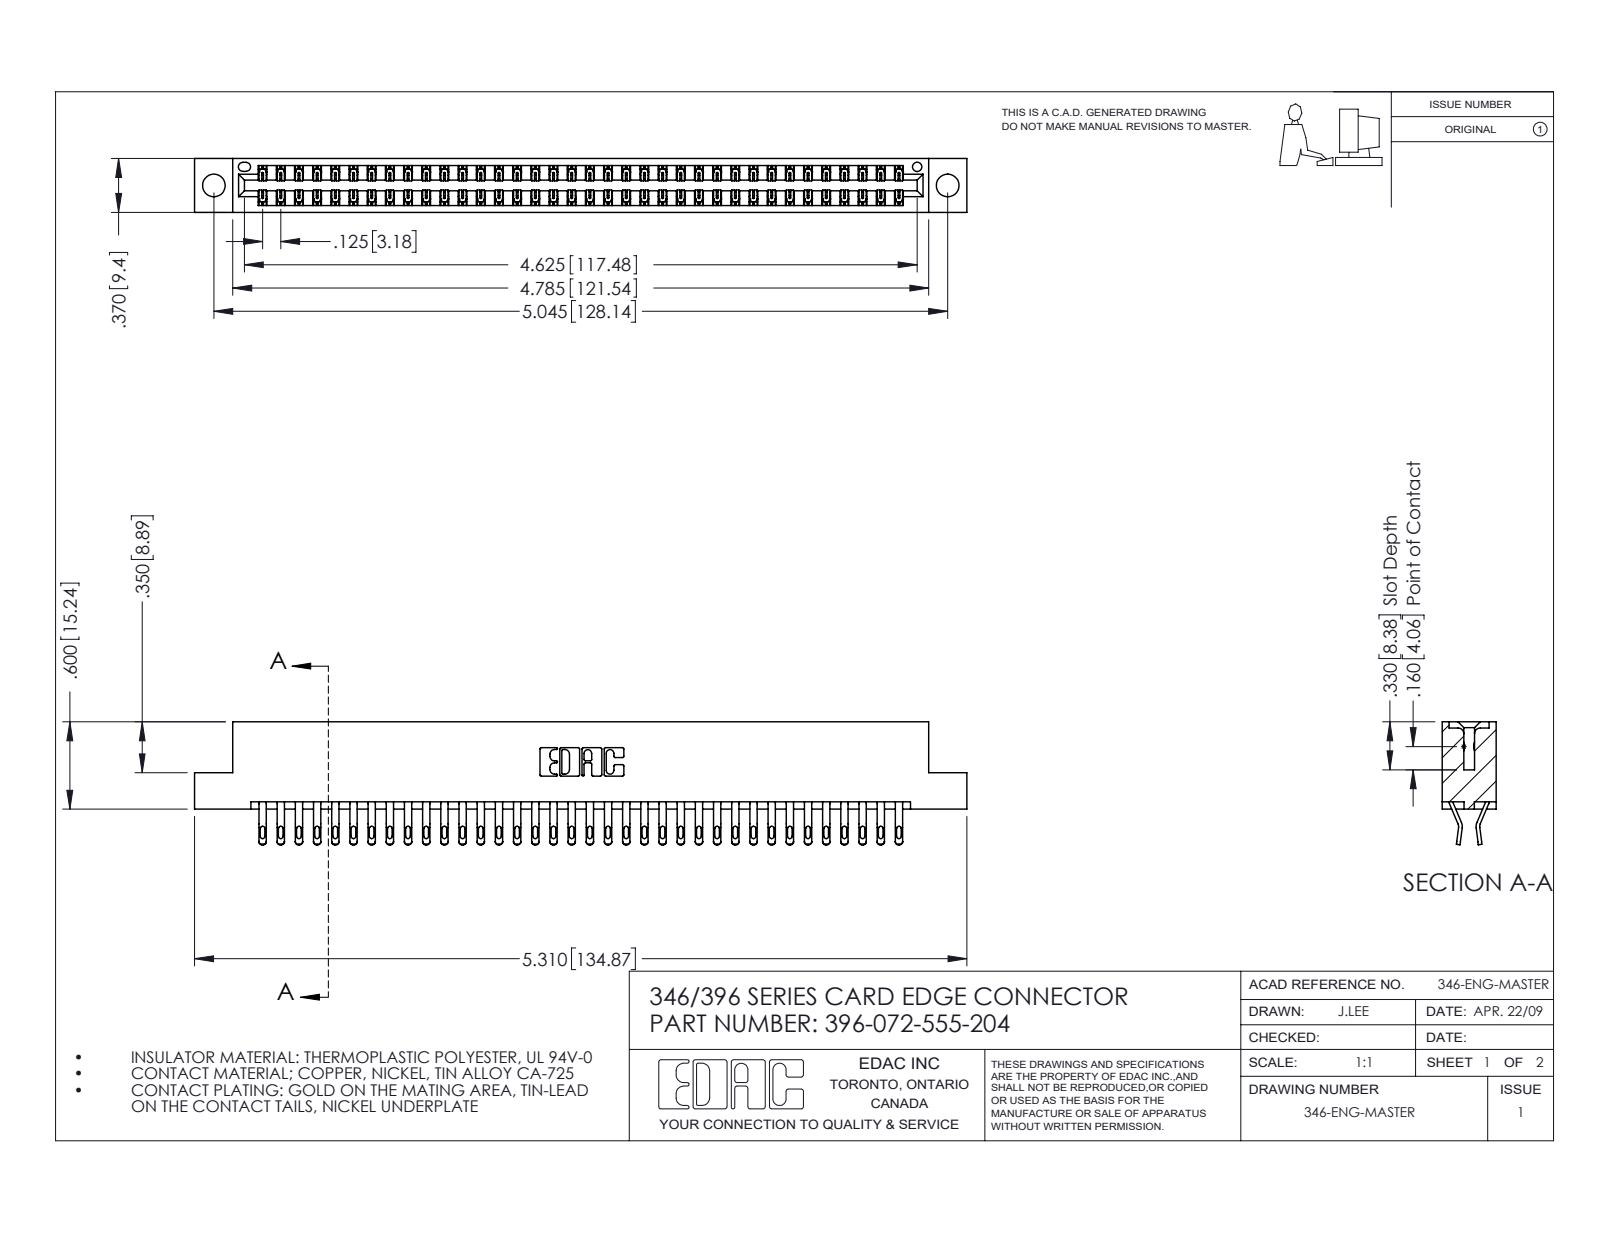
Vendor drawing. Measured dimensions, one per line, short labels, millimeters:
name: 396-072-555-204; 345-292-001_555 Tail; 346 Part_Flush Mounting Lugs - 0.156 Dia-TH
written by: SolidWorks 2016 (CONFIG_CONTROL_DESIGN)
unit: mm
bodies: 73 solids, 4298 faces (2452 planar, 1846 cylindrical, 0 other)
size: 134.9 × 21.5 × 9.4
volume: 13 200 mm³; area: 18 650 mm²
holes: 2× ⌀4, 1× ⌀1.6
rounds: 144× R0.4, 144× R0.5, 108× R0.2, 22× R0.3, 6× R0.2, 6× R0.8, 3× R0.7, 2× R0.3
face distances: 1.2, 8.2, 9.4, 6.4, 0.6, 1.8, 7.6, 7, 3.8, 5.6
hole spacings: 6.2, 122.8, 128.1
